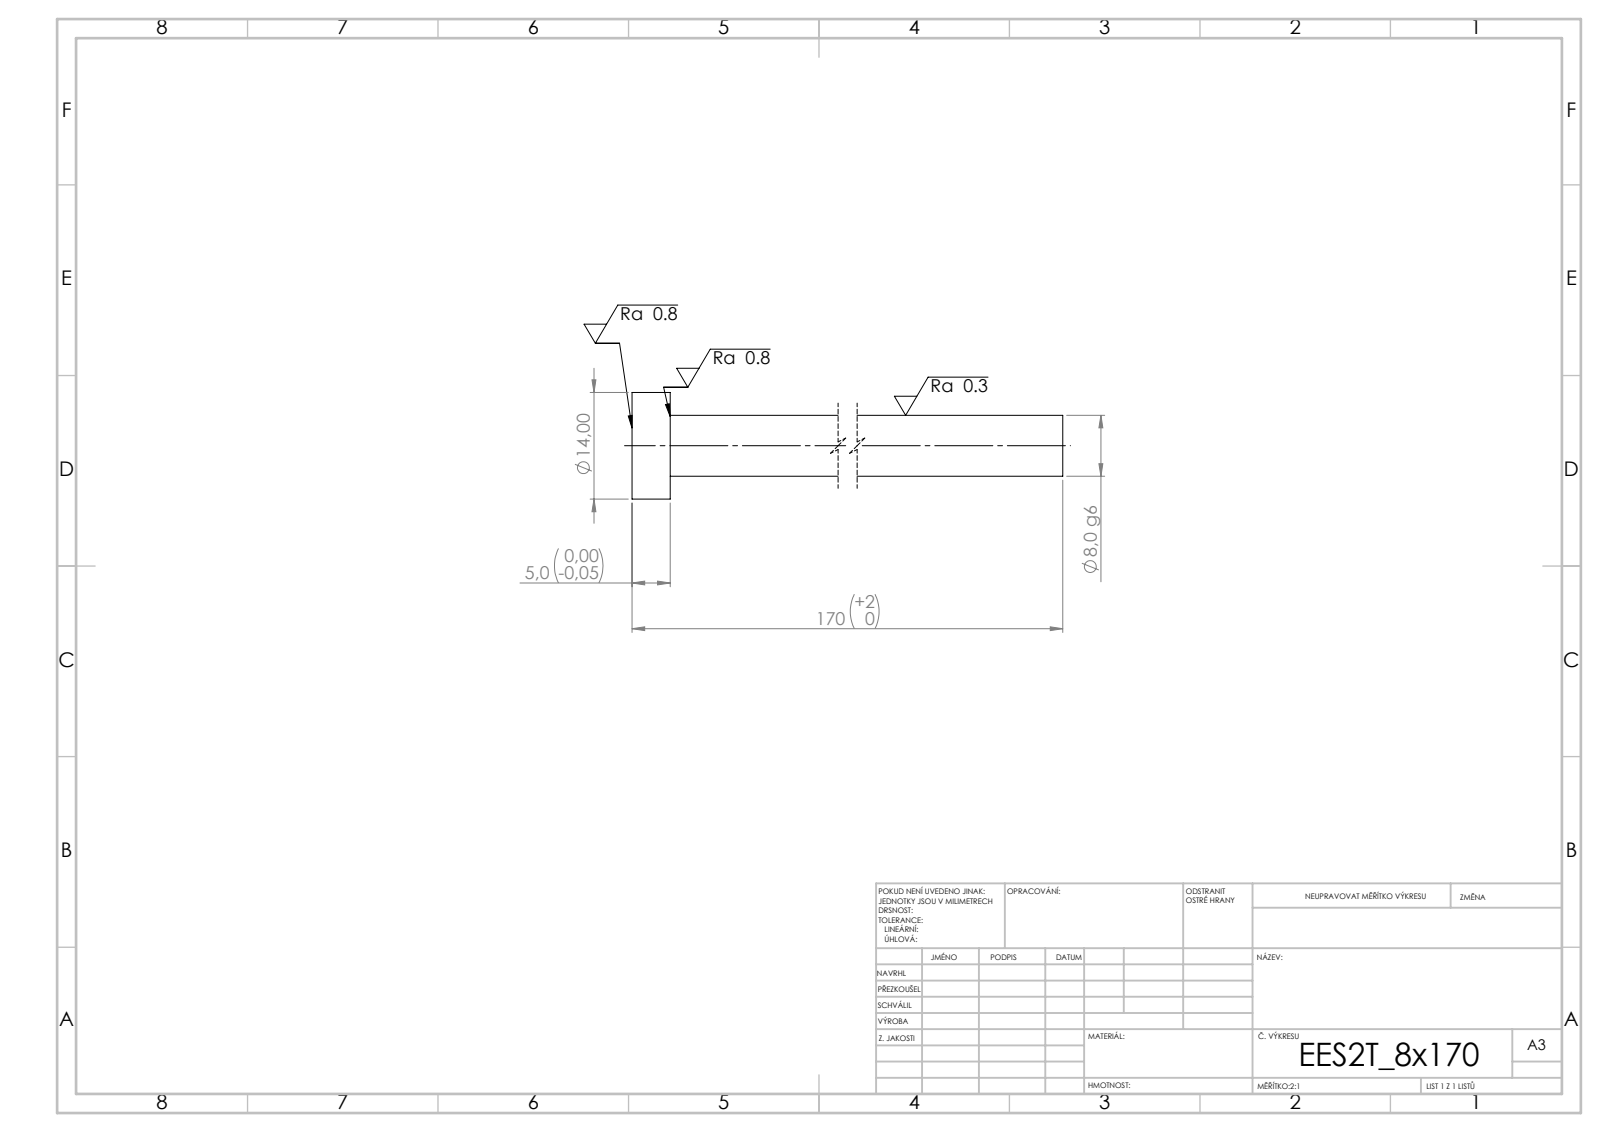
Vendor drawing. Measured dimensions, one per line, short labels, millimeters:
written by: SolidWorks 2019 (CONFIG_CONTROL_DESIGN)
unit: mm
bodies: 1 solid, 7 faces (3 planar, 4 cylindrical, 0 other)
size: 170 × 14 × 14
volume: 9 063 mm³; area: 4 675 mm²
bosses: 1× ⌀14, 1× ⌀8
face distances: 5, 170, 165
